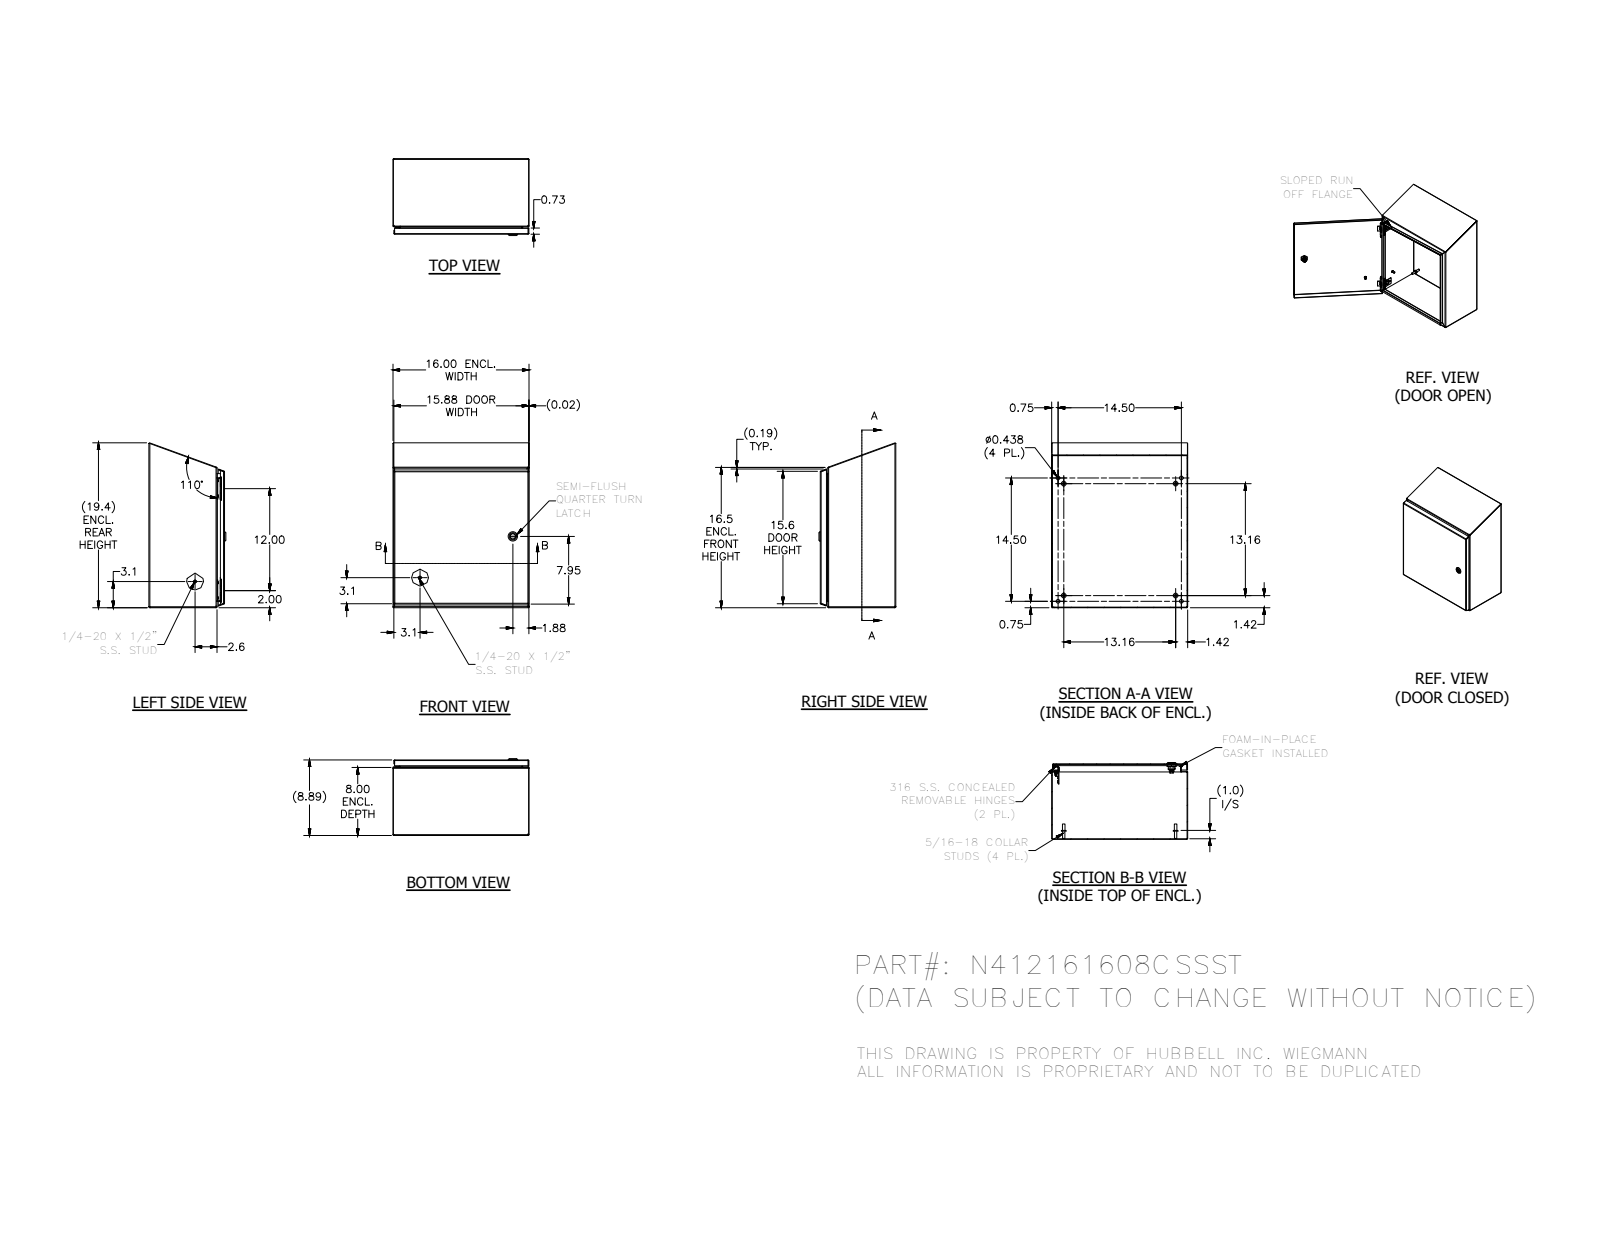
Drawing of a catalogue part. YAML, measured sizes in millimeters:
part_name: "N412161608CSSST"
step_written_by: "SolidWorks 2018 (AUTOMOTIVE_DESIGN)"
units: millimeters
bodies: {solids: 36, faces: 1426, planar: 538, cylindrical: 509, other: 379}
overall_size: [492.5, 406.4, 229.7]
volume: 1524000
surface_area: 1634000
round_holes:
  - {diameter: 2.4, count: 4}
  - {diameter: 3.9, count: 4}
  - {diameter: 4.2, count: 4}
  - {diameter: 4.4, count: 4}
  - {diameter: 4.7, count: 4}
  - {diameter: 11.1, count: 4}
  - {diameter: 4, count: 3}
  - {diameter: 4.7, count: 1}
  - {diameter: 5, count: 1}
  - {diameter: 8, count: 1}
  - {diameter: 10, count: 1}
  - {diameter: 10.2, count: 1}
round_bosses_or_shafts:
  - {diameter: 6.4, count: 10}
  - {diameter: 14.3, count: 4}
  - {diameter: 9.1, count: 4}
  - {diameter: 8.1, count: 4}
  - {diameter: 7.6, count: 4}
  - {diameter: 7, count: 4}
  - {diameter: 6.5, count: 4}
  - {diameter: 4.2, count: 4}
partial_cylinders:
  - {radius: 0.8, count: 29}
  - {radius: 1.3, count: 26}
  - {radius: 2.7, count: 19}
  - {radius: 0.4, count: 18}
  - {radius: 0.5, count: 16}
  - {radius: 3.2, count: 16}
  - {radius: 0.8, count: 8}
  - {radius: 13.3, count: 6}
face_to_face_distances: [1.9, 223.9, 404.5, 222, 225.7, 402.6, 406.4, 201.3, 22.5, 20.7]
hole_center_spacings: [304.8, 368.3, 375.3, 12.7, 16.7, 16.8, 24.2, 33.2]
